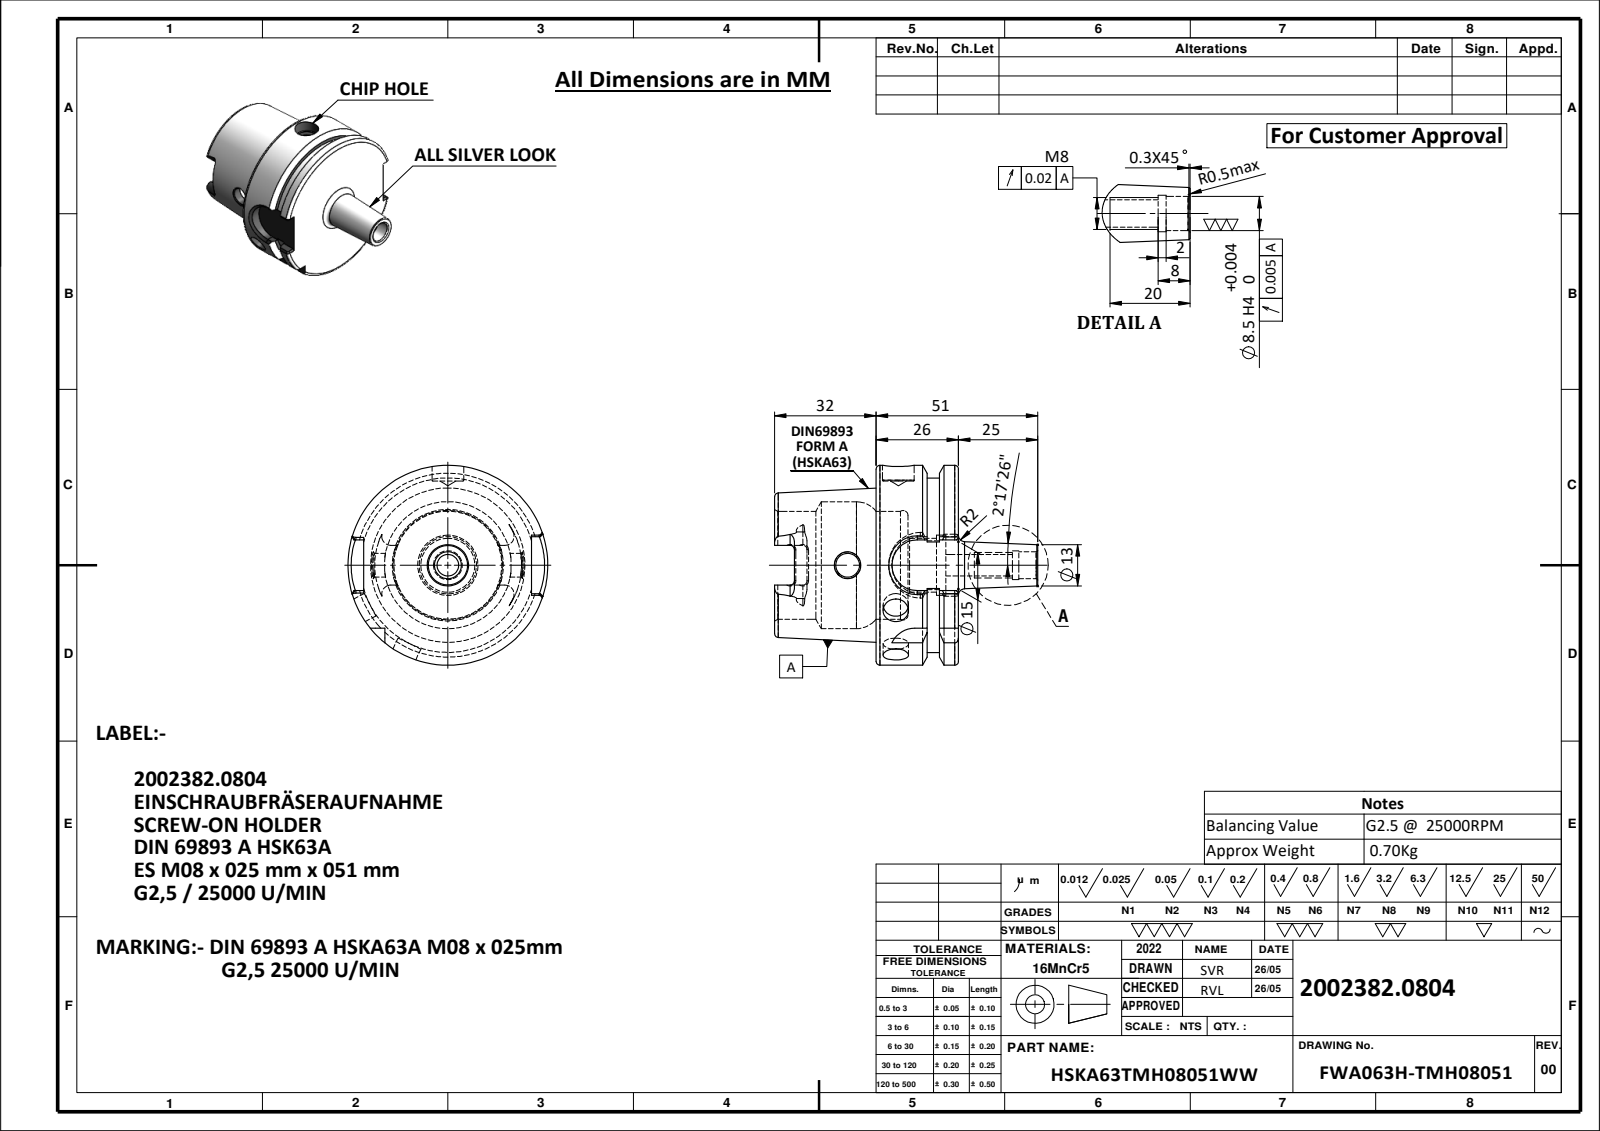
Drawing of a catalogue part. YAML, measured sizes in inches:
part_name: "HSKA63TMS08051WW; FWA063H-TMH08051"
step_written_by: "SolidWorks 2024 (CONFIG_CONTROL_DESIGN)"
units: inches
bodies: {solids: 1, faces: 164, planar: 51, cylindrical: 49, other: 64}
overall_size: [3.266, 2.48, 2.48]
volume: 5.107
surface_area: 37.14
round_holes:
  - {diameter: 0.315, count: 2}
  - {diameter: 0.268, count: 1}
  - {diameter: 0.295, count: 1}
  - {diameter: 0.335, count: 1}
  - {diameter: 0.358, count: 1}
  - {diameter: 0.394, count: 1}
  - {diameter: 0.669, count: 1}
  - {diameter: 0.748, count: 1}
  - {diameter: 1.339, count: 1}
  - {diameter: 1.575, count: 1}
round_bosses_or_shafts:
  - {diameter: 2.48, count: 1}
  - {diameter: 2.165, count: 1}
partial_cylinders:
  - {radius: 0.051, count: 6}
  - {radius: 0.113, count: 4}
  - {radius: 0.315, count: 2}
  - {radius: 0.354, count: 1}
face_to_face_distances: [1.022, 0.394, 0.628, 1.26, 1.654, 2.281, 2.083, 2.126, 0.866, 0.472]
